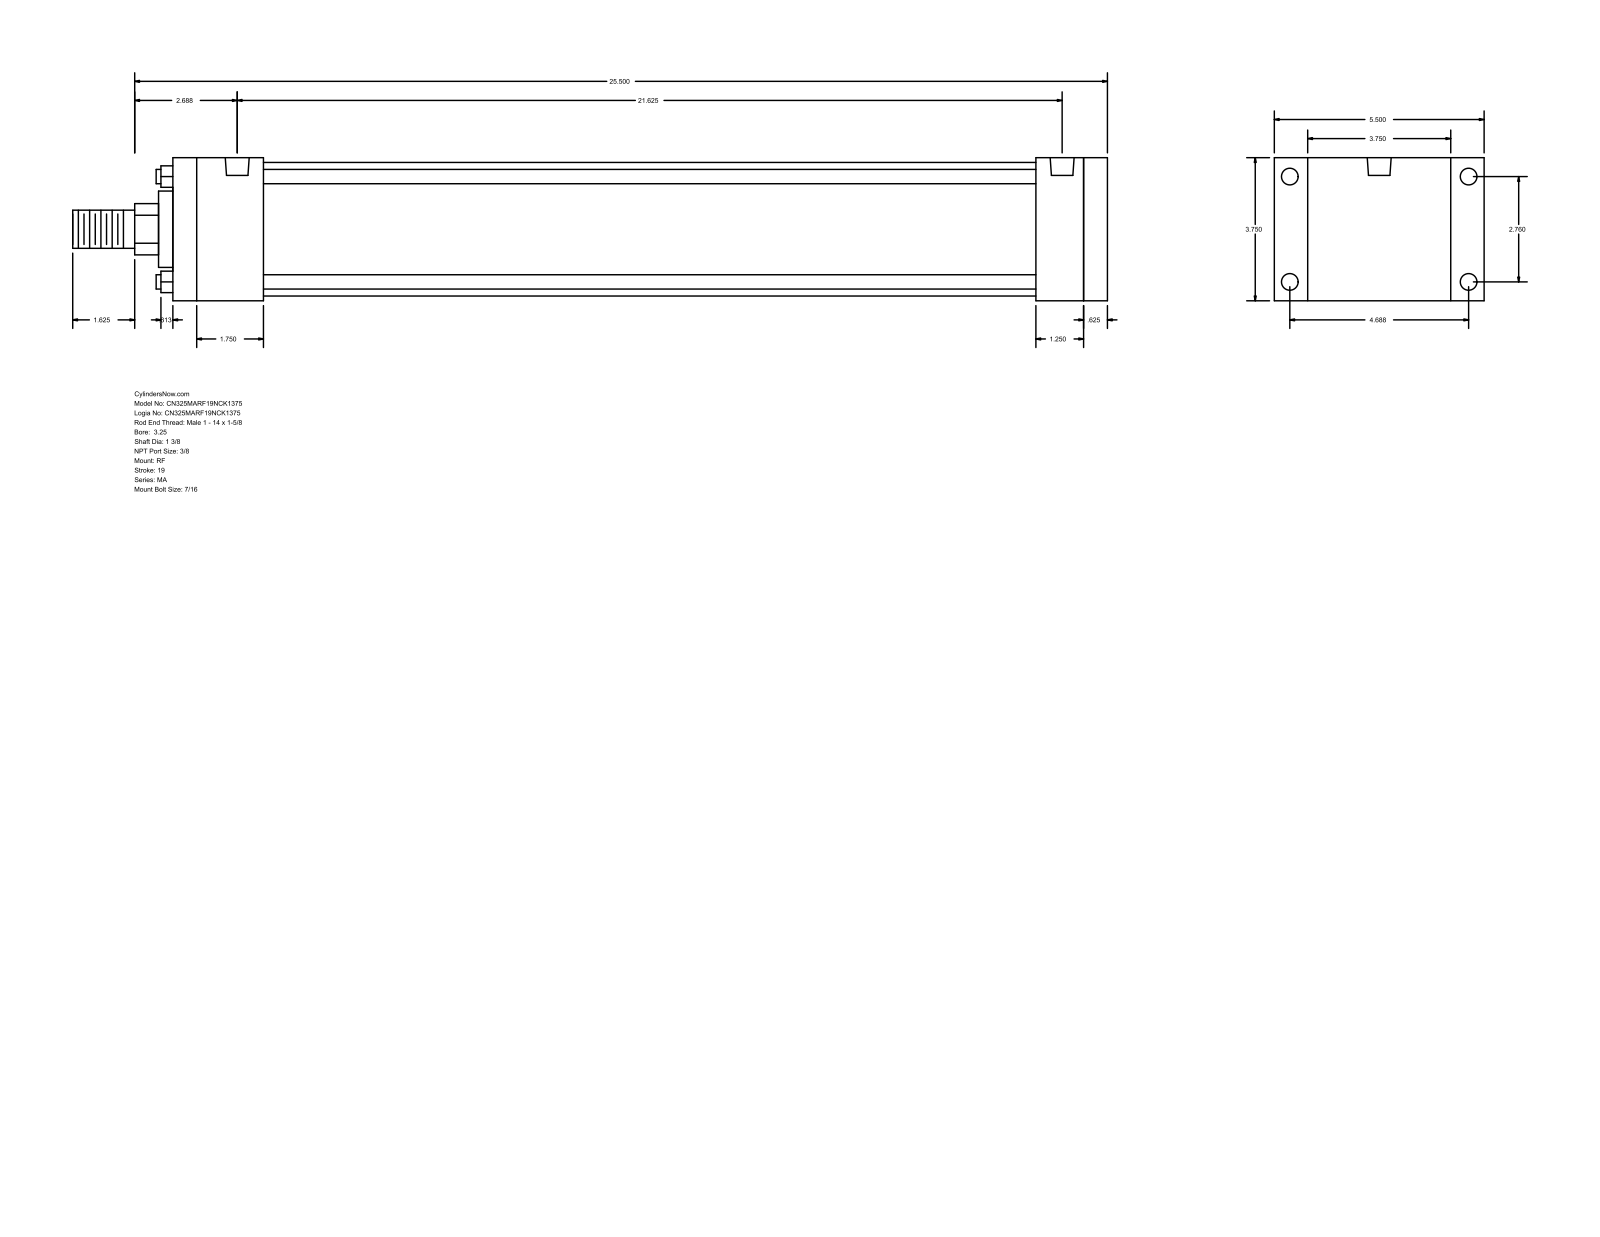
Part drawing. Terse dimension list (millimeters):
name: MA_RF__0325_1.375
written by: GSSL Pune (CONFIG_CONTROL_DESIGN)
unit: mm
bodies: 0 solids, 92 faces (64 planar, 28 cylindrical, 0 other)
size: 688.98 × 139.7 × 95.25
holes: 8× ⌀11.11, 2× ⌀15.93
bosses: 4× ⌀9.53, 1× ⌀88.9, 1× ⌀50.8, 1× ⌀34.92, 1× ⌀25.4
rounds: 1× R17.06
face distances: 95.24, 622.3, 606.43, 15.87, 22.23, 117.47, 574.68, 31.75, 47.62, 60.32
hole spacings: 4.77, 70.1, 119.06, 138.16, 539.74, 544.51, 549.28
